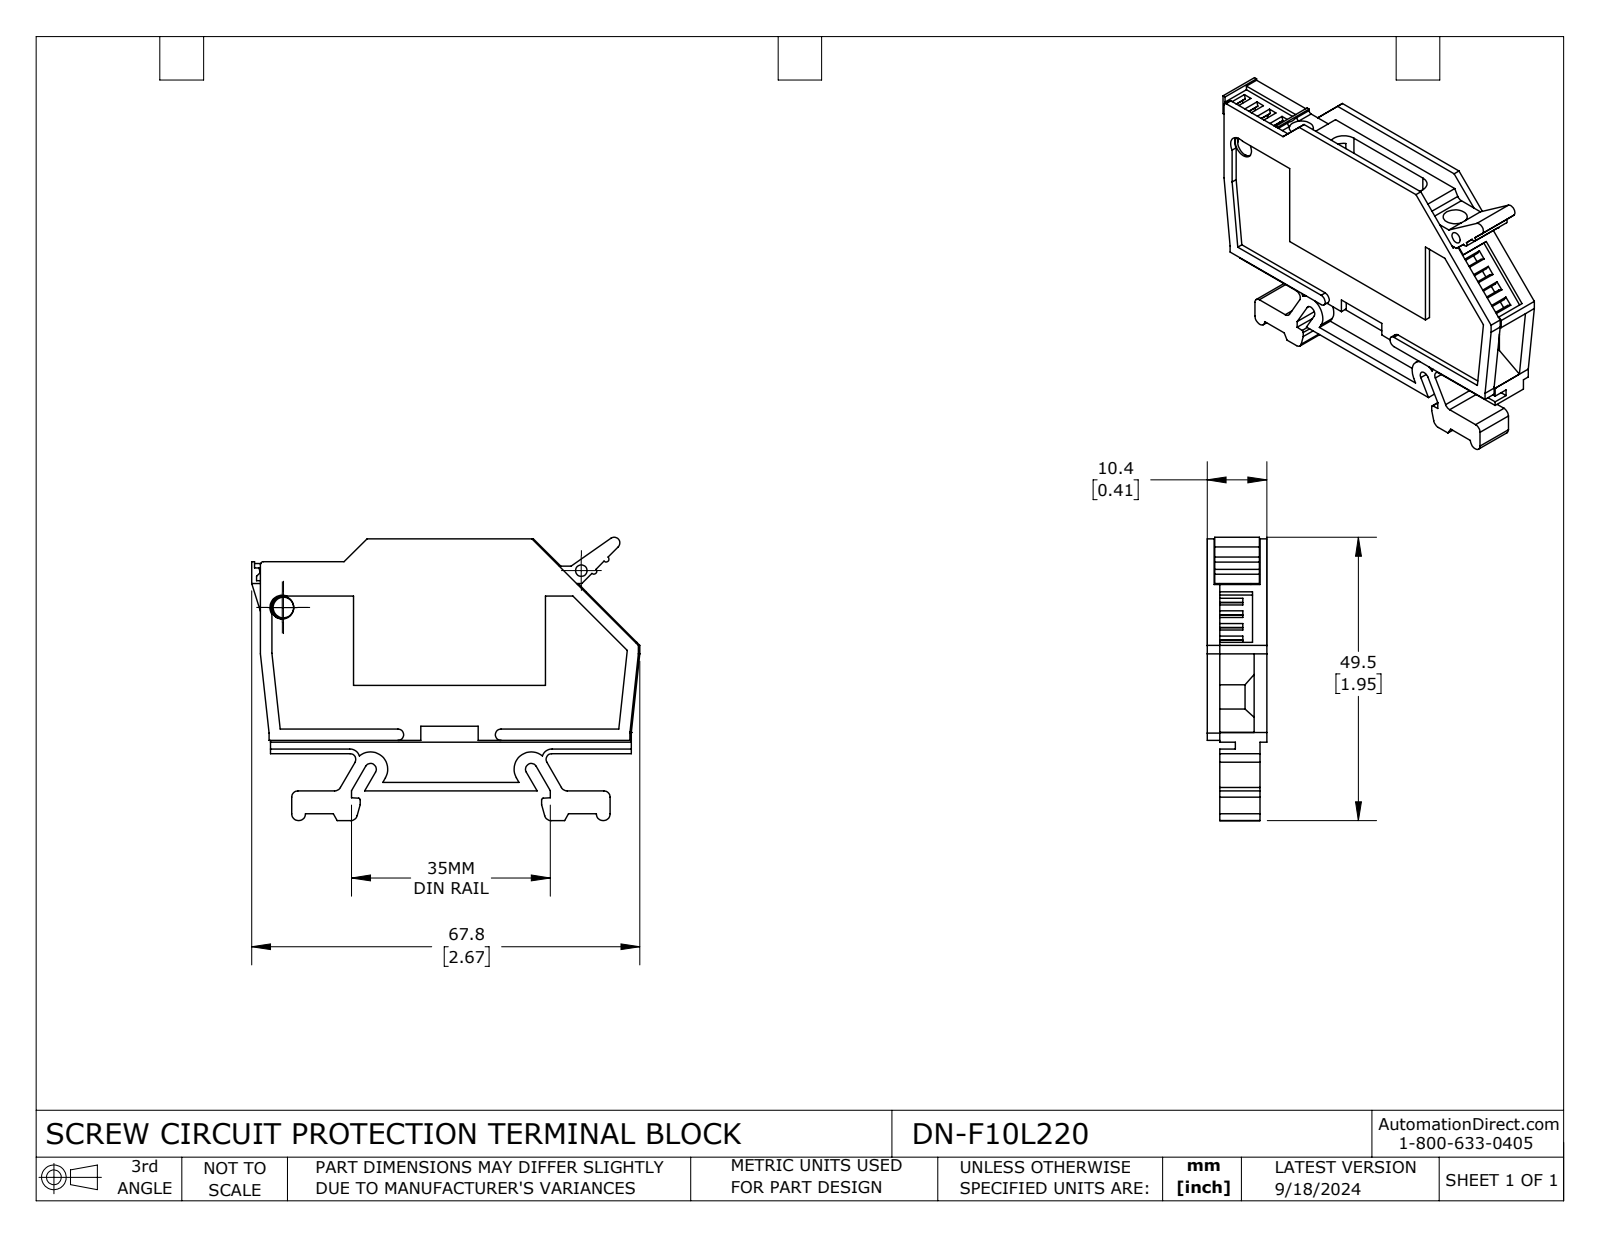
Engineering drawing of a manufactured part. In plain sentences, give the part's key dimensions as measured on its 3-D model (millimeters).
The part is named "DN-F10L220". Its 3-D file was written by "SolidWorks 2023 (CONFIG_CONTROL_DESIGN)". It is 1 solid with 440 faces: 292 planar, 78 cylindrical and 70 other. Overall it measures 67.8 by 49.5 by 10.4 millimeters. Its volume is 14 800 cubic millimeters and its surface area 13 920 square millimeters. Round holes: 3 of diameter 4.2, 2 of diameter 2, 1 of diameter 2.5, 1 of diameter 4. Round bosses or shafts: 1 of diameter 4. Partial cylindrical surfaces (rounded edges, fillets, slot ends): 12 of radius 1, 6 of radius 1.2, 4 of radius 0.5, 3 of radius 1.2, 3 of radius 2, 2 of radius 0.3, 2 of radius 1.1, 2 of radius 1.8. The main face-to-face distances are 1.2, 1, 9.1, 8.2, 9.2, 2.2, 7.9, 2, 1.3, 8.1. The hole center spacings are 21, 21, 38, 52.4, 52.6, 54.6.
